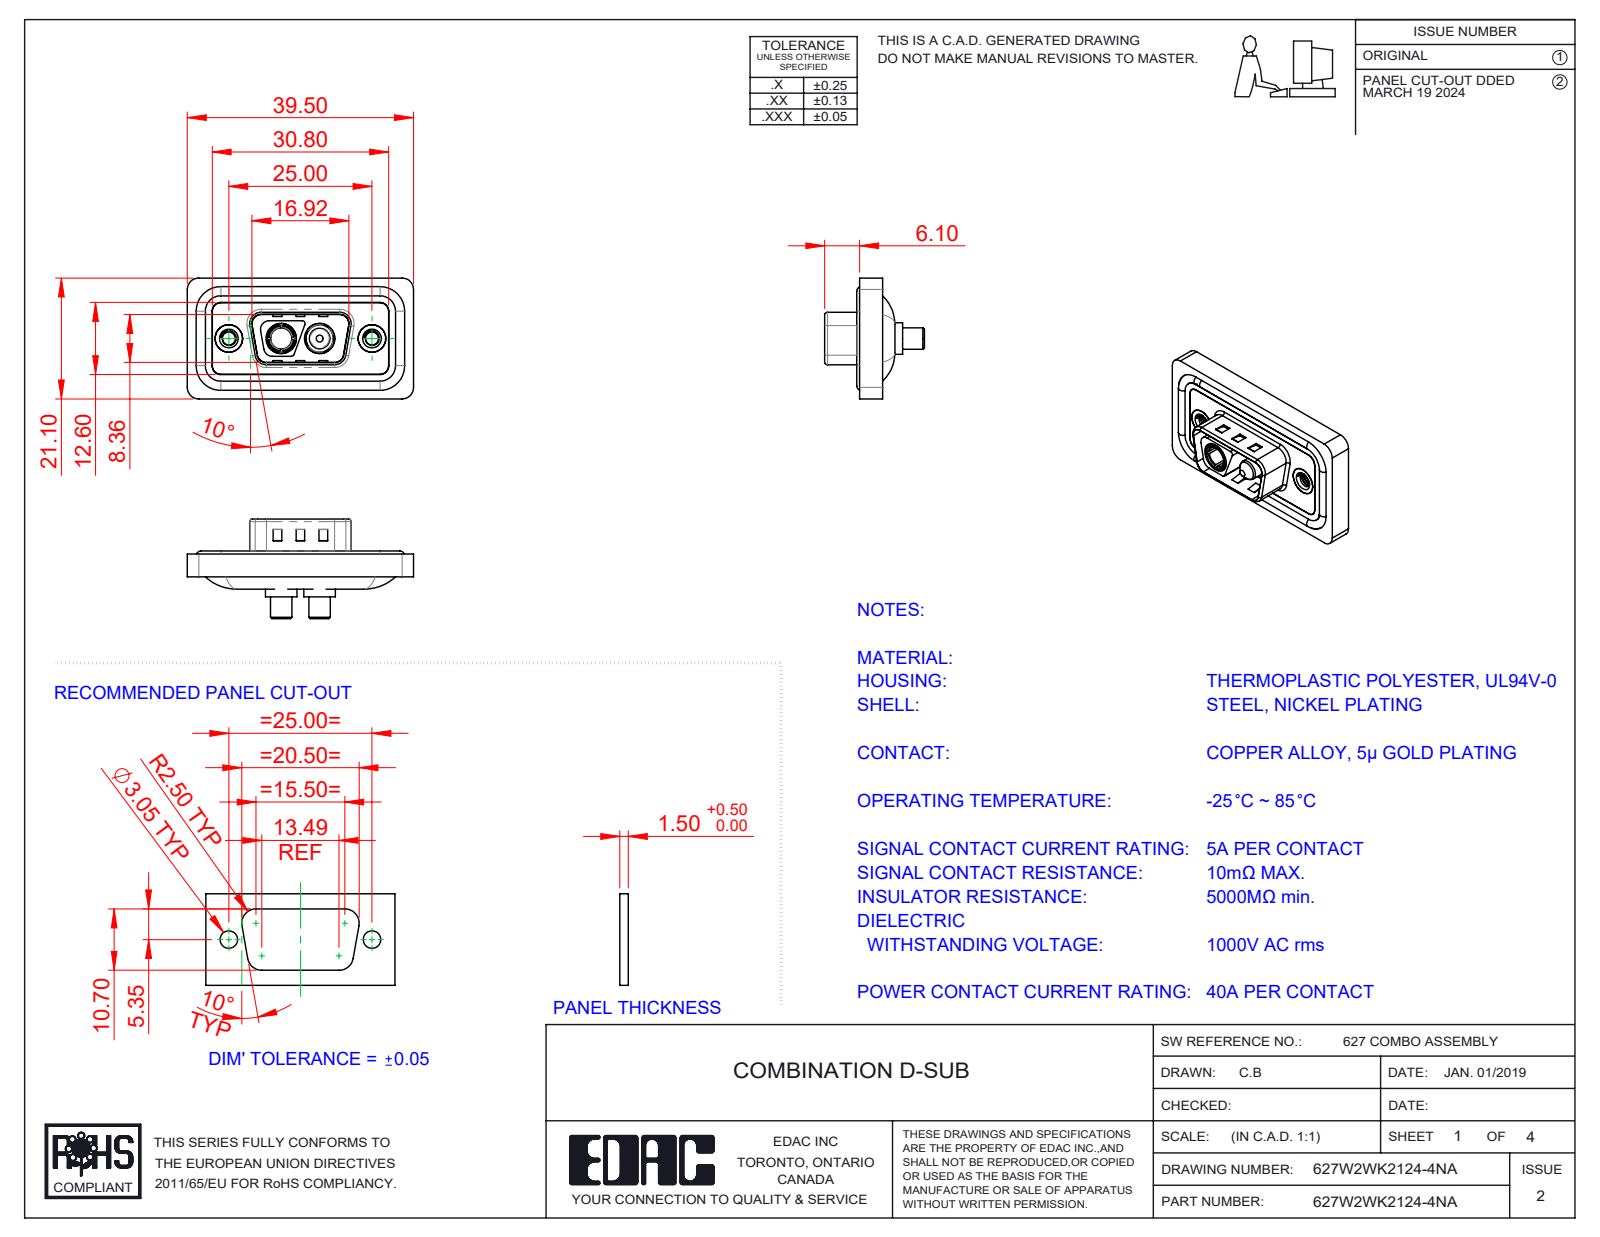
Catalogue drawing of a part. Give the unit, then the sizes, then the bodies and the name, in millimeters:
Units: millimetres
Overall size (bounding box): 39.5 × 21.1 × 17.4
Round holes (diameter × count): ⌀2.26 ×2, ⌀4 ×2, ⌀4.8 ×2, ⌀4.85 ×2, ⌀5 ×2, ⌀5.3 ×2, ⌀3.7 ×1
Round bosses / shafts (diameter × count): ⌀1.6 ×4, ⌀5.5 ×2, ⌀5.2 ×2, ⌀4.9 ×2, ⌀4.75 ×2, ⌀3.75 ×2, ⌀4.96 ×1, ⌀3.6 ×1
Partial cylindrical surfaces — rounded edges, fillets, slot ends (radius × count): R1.5 ×24, R2 ×18, R0.5 ×10, R1.6 ×8, R0.25 ×4, R0.6 ×4, R0.65 ×4, R0.9 ×4
Main face-to-face distances: 0.4, 1.1, 2.9, 0.5, 3.1, 1.6, 1.5, 2.5, 4, 1.8
Hole centre spacings: 9.14, 15.86, 6.72, 25
Volume: 4 593 mm³ · Surface area: 7 362 mm²
Bodies: 11 solids, 532 faces (189 planar, 229 cylindrical, 114 other)
Part name (STEP PRODUCT): 627Combo Housing_2WK2; 627W2WK2124-4NA; 627Combo Shell Rear_09 Contacts; Power Pin_40A S (+4 more)
STEP written by: SolidWorks 2023 (CONFIG_CONTROL_DESIGN)
